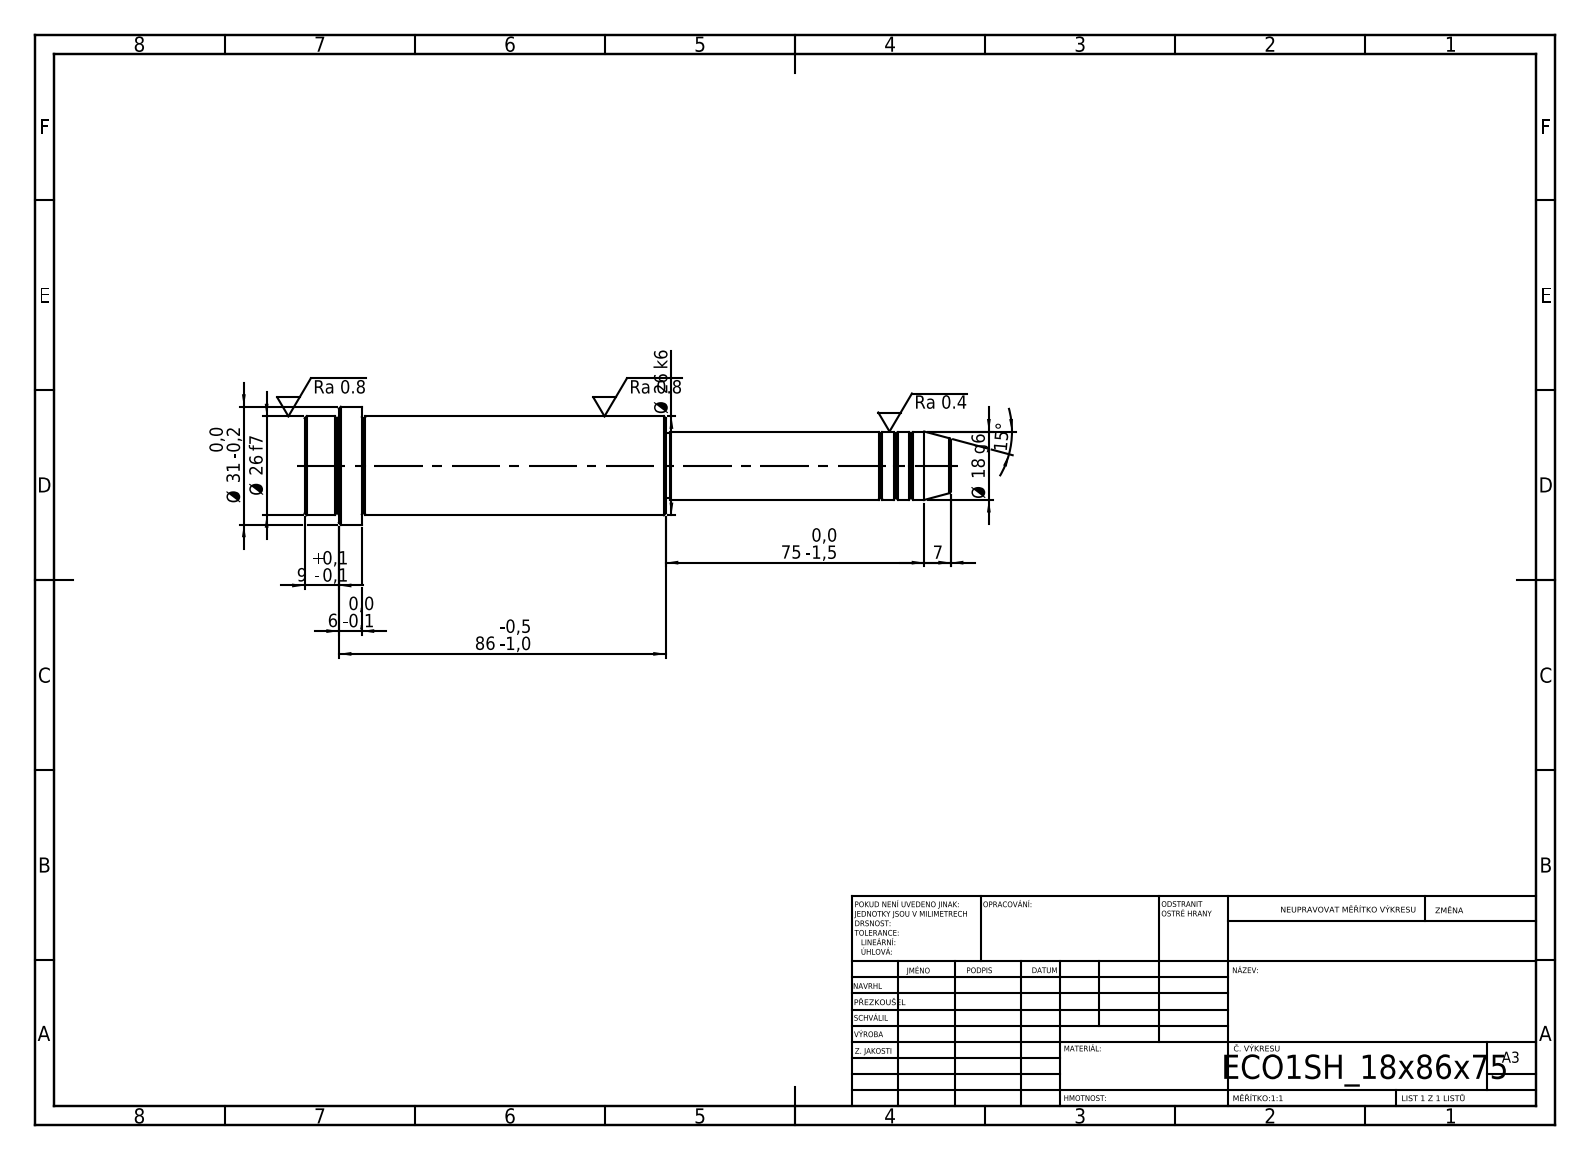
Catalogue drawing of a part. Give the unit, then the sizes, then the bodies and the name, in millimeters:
Units: millimetres
Overall size (bounding box): 170 × 31 × 31
Round bosses / shafts (diameter × count): ⌀31 ×1, ⌀26 ×1, ⌀18 ×1, ⌀17 ×1
Main face-to-face distances: 95, 80, 15, 86, 6, 9, 75, 155, 161, 170
Volume: 70 332 mm³ · Surface area: 13 625 mm²
Bodies: 1 solid, 52 faces (6 planar, 16 cylindrical, 30 other)
STEP written by: SolidWorks 2019 (CONFIG_CONTROL_DESIGN)
